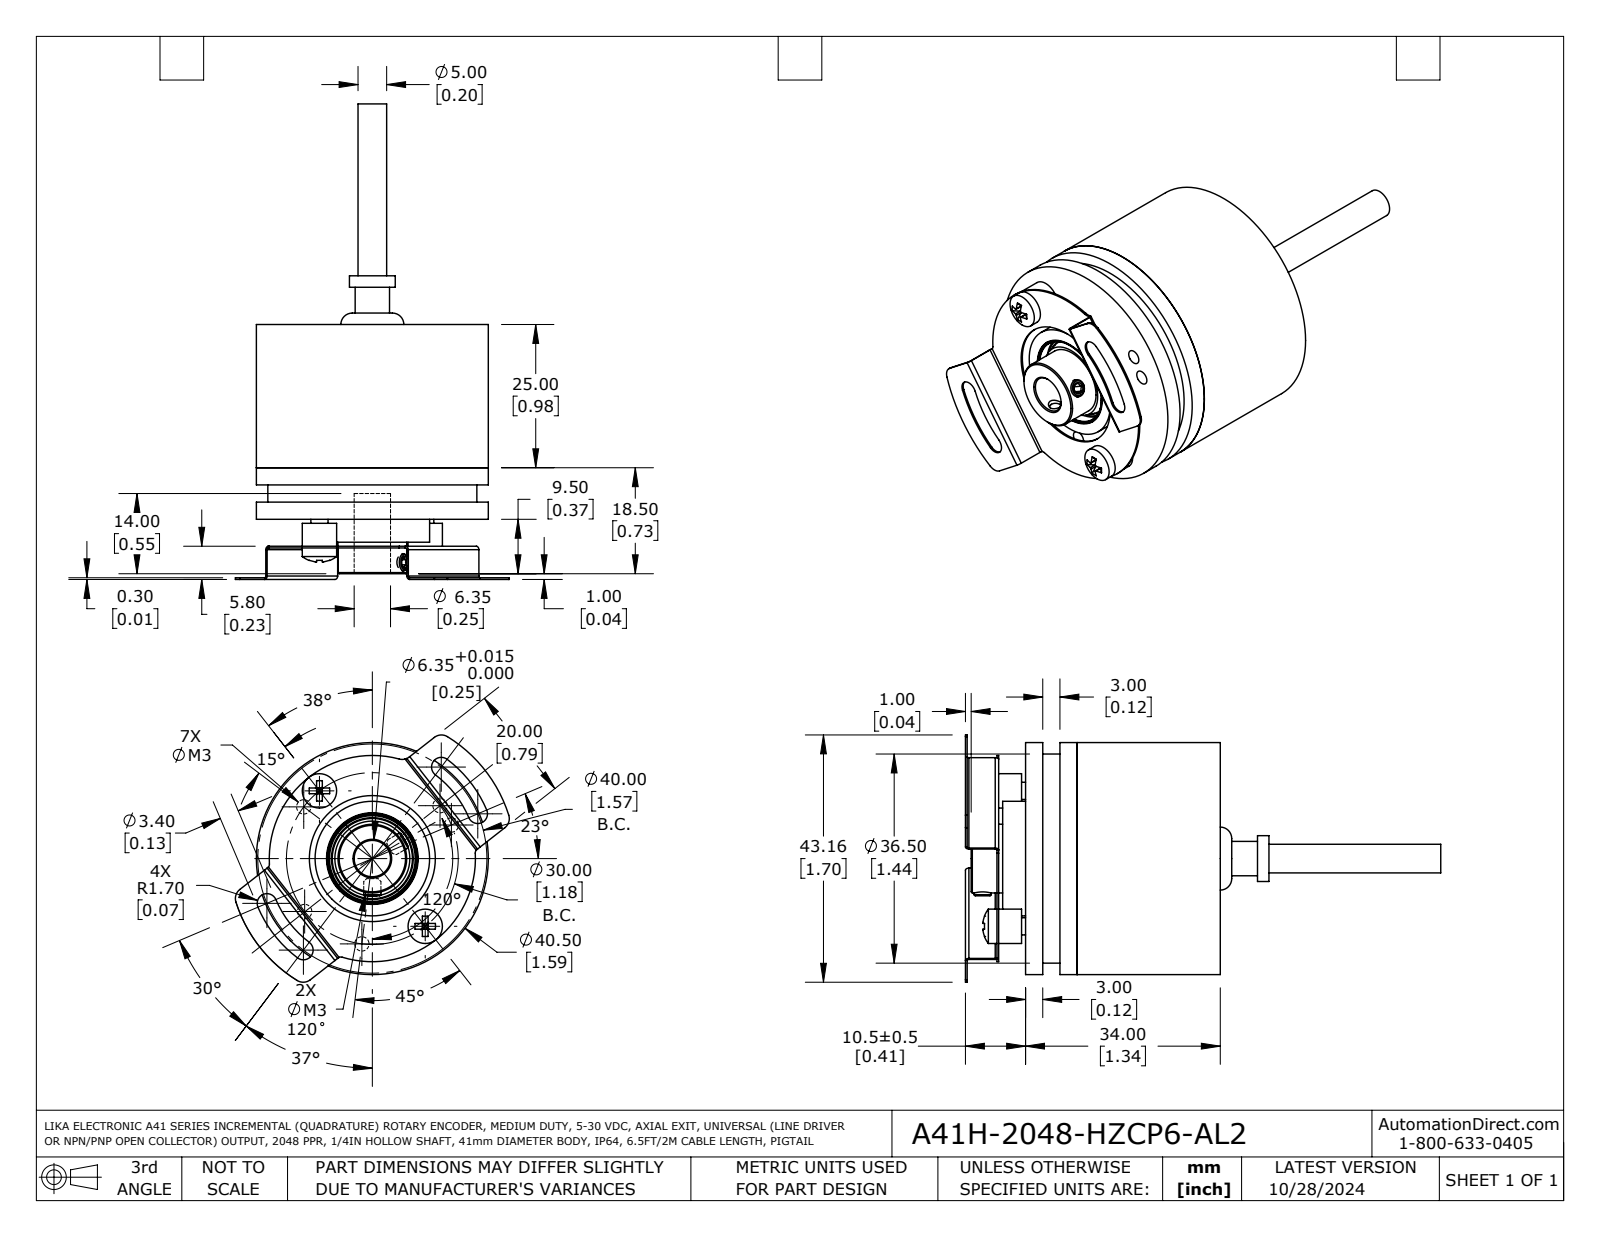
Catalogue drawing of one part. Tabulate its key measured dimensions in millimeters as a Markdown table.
| quantity | value |
| --- | --- |
| part name | A41H-2048-HZCP6-AL2 |
| STEP written by | SolidWorks 2021 (AUTOMOTIVE_DESIGN) |
| units | millimeters |
| bodies | 15 solids, 465 faces (139 planar, 186 cylindrical, 140 other) |
| overall size | 83 × 47.8 × 43.2 |
| volume | 19 450 mm³ |
| surface area | 20 890 mm² |
| round holes (diameter × count) | 2.5 × 9, 1.6 × 7, 4 × 3, 2.2 × 2, 3.2 × 2, 3.5 × 2, 4.3 × 1, 6.4 × 1, 7.5 × 1, 13 × 1, 15.3 × 1, 15.5 × 1 |
| round bosses / shafts (diameter × count) | 3 × 4, 6 × 3, 3.8 × 2, 2 × 2, 40.5 × 1, 38 × 1, 37 × 1, 36.5 × 1 |
| partial cylindrical surfaces (radius × count) | 1 × 14, 0.2 × 8, 2 × 5, 0.3 × 4, 0.6 × 4, 1.7 × 4, 0.8 × 3, 18 × 1 |
| main face-to-face distances | 3, 11, 34, 23, 5, 31, 2, 22, 1, 20 |
| hole center spacings | 15, 17, 21.2, 2.8, 3, 21.3, 24, 26 |
